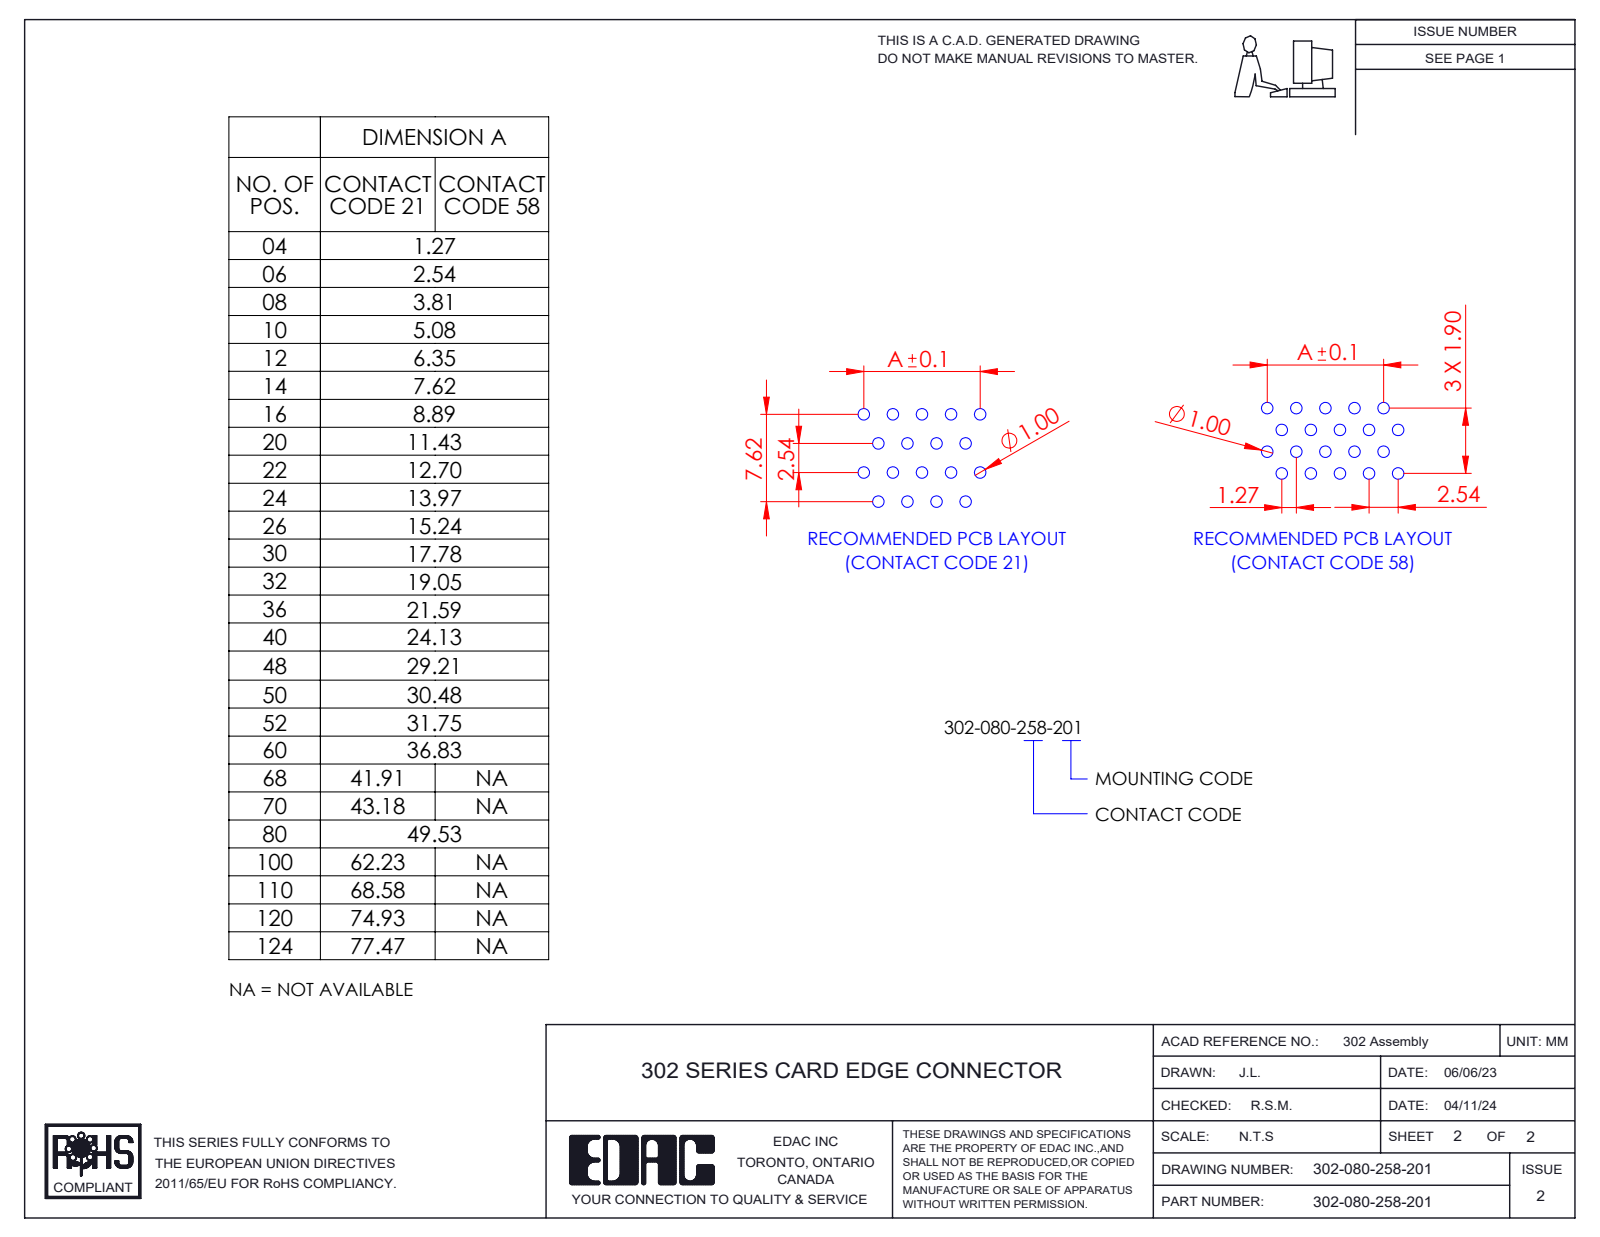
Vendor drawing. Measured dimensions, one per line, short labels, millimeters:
name: Contact_302-290-X58-003; 302-080-258-201; Contact_302-290-X58-004; Contact_302-290-X58-001 (+2 more)
written by: SolidWorks 2023 (CONFIG_CONTROL_DESIGN)
unit: mm
bodies: 81 solids, 4227 faces (3007 planar, 1056 cylindrical, 164 other)
size: 56.9 × 21.37 × 11.68
volume: 5 033 mm³; area: 14 435 mm²
rounds: 88× R0.2, 80× R0.25, 4× R0.5, 3× R2.03, 2× R0.11, 2× R0.4, 2× R0.41, 2× R0.8
face distances: 1.27, 2.54, 3.81, 5.08, 1.9, 7.62, 6.35, 8.88, 8.89, 10.16
